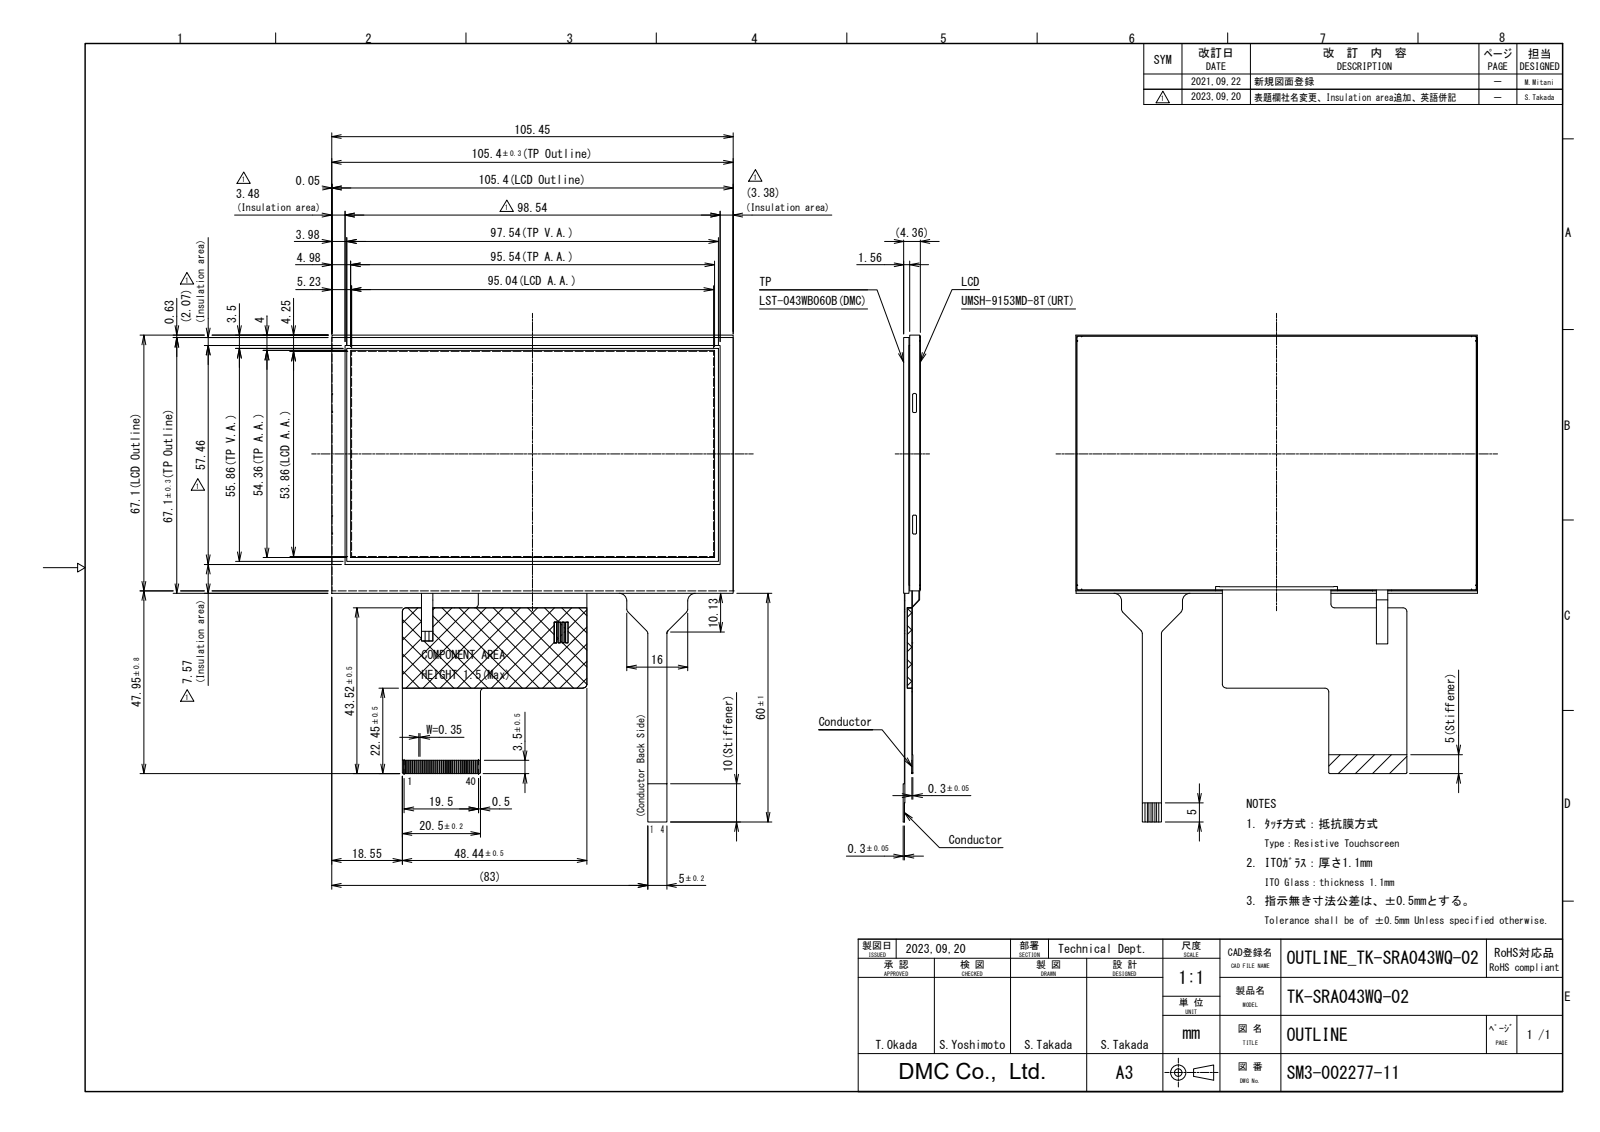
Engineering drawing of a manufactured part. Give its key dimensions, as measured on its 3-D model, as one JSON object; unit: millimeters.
{"part_name": "HP_TK-SRA043WQ-02", "step_written_by": "Autodesk Inventor 2020 (AUTOMOTIVE_DESIGN)", "units": "millimeters", "bodies": {"solids": 1, "faces": 637, "planar": 564, "cylindrical": 73, "other": 0}, "overall_size": [127.73, 105.45, 4.47], "volume_mm3": 29921, "surface_area_mm2": 48584, "partial_cylinders_radius": [[0.3, 43], [1, 8], [0.5, 6], [2, 2]], "face_to_face_distances": [1.3, 4.36, 1.25, 2.96, 1.4, 1.66, 3.06, 1.5, 1.55, 2.8]}
